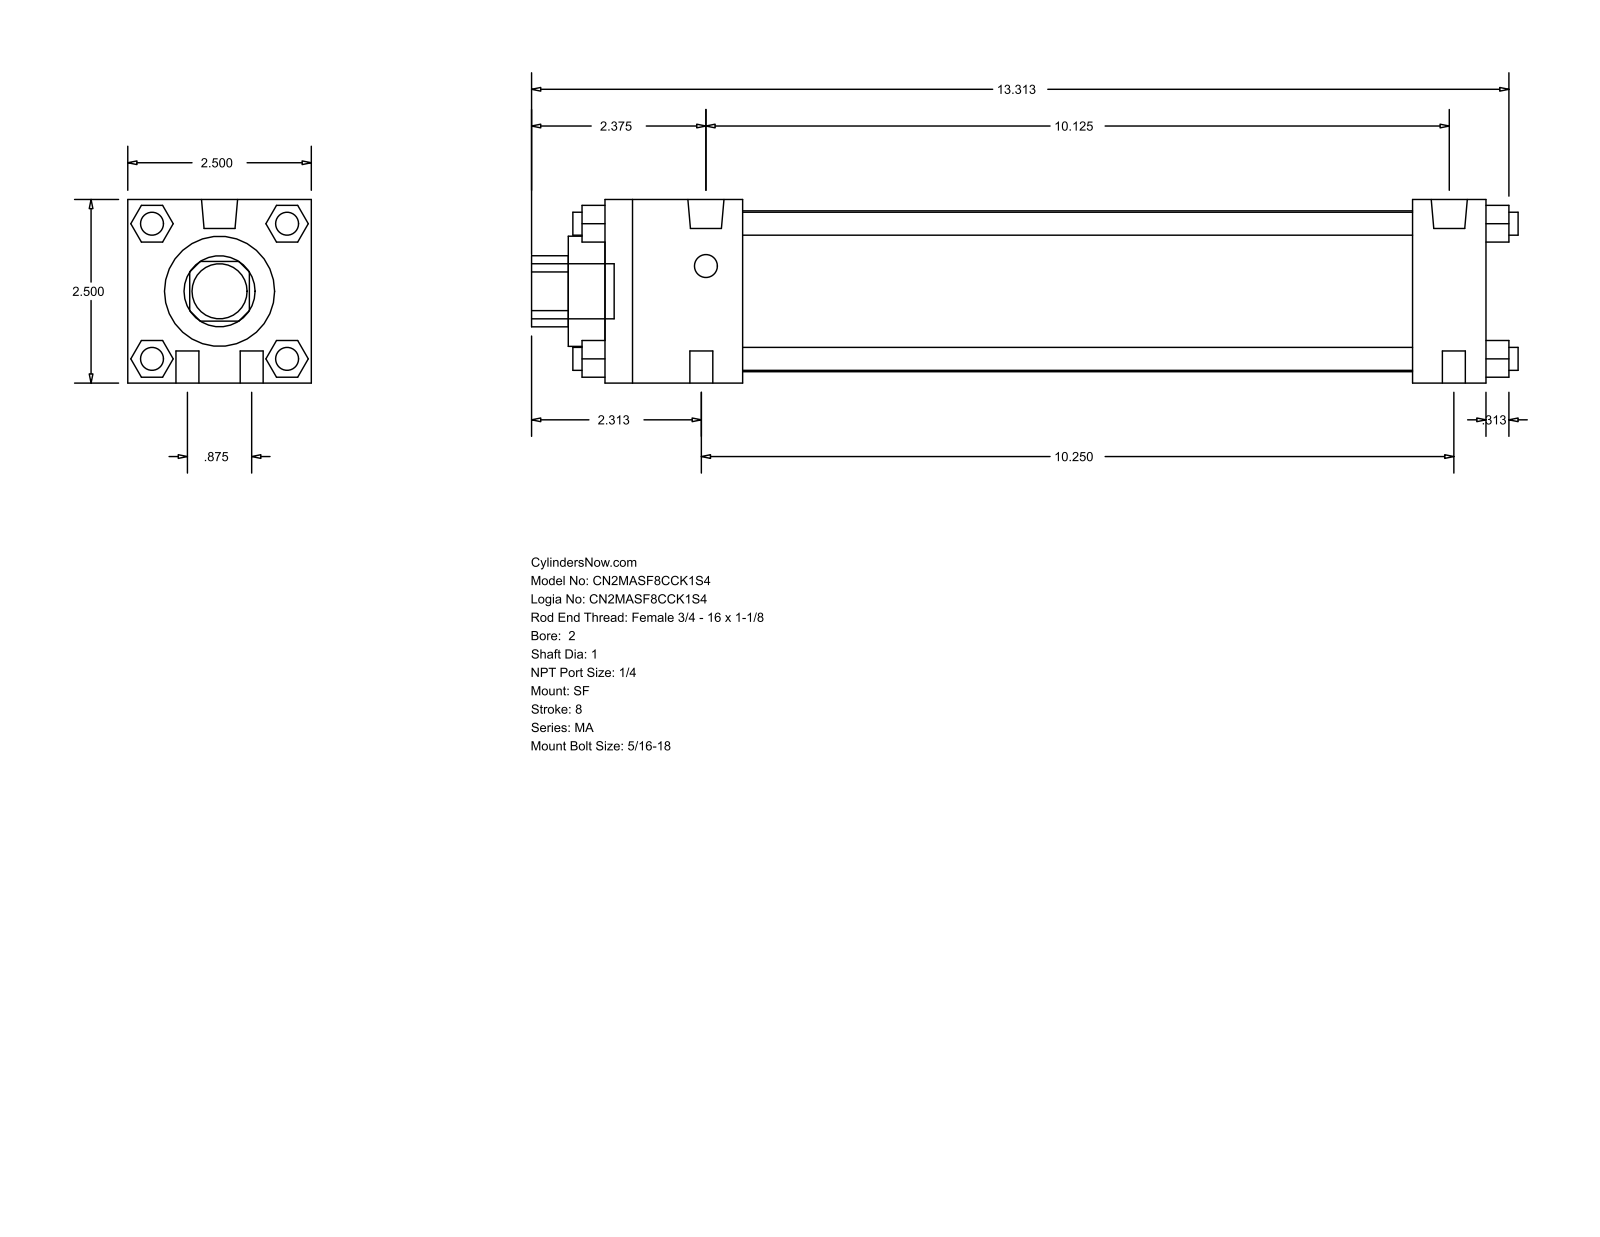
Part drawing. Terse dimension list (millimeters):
name: MA_SF__0200_1
written by: GSSL Pune (CONFIG_CONTROL_DESIGN)
unit: mm
bodies: 0 solids, 124 faces (94 planar, 30 cylindrical, 0 other)
size: 341.31 × 63.5 × 63.5
holes: 1× ⌀25.4, 1× ⌀38.1, 1× ⌀55.63
bosses: 10× ⌀7.94, 2× ⌀12.49, 1× ⌀19.05
rounds: 1× R12.29
face distances: 63.5, 304.8, 12.7, 25.4, 279.4, 47.63, 231.77, 257.17, 40.47, 23.37
